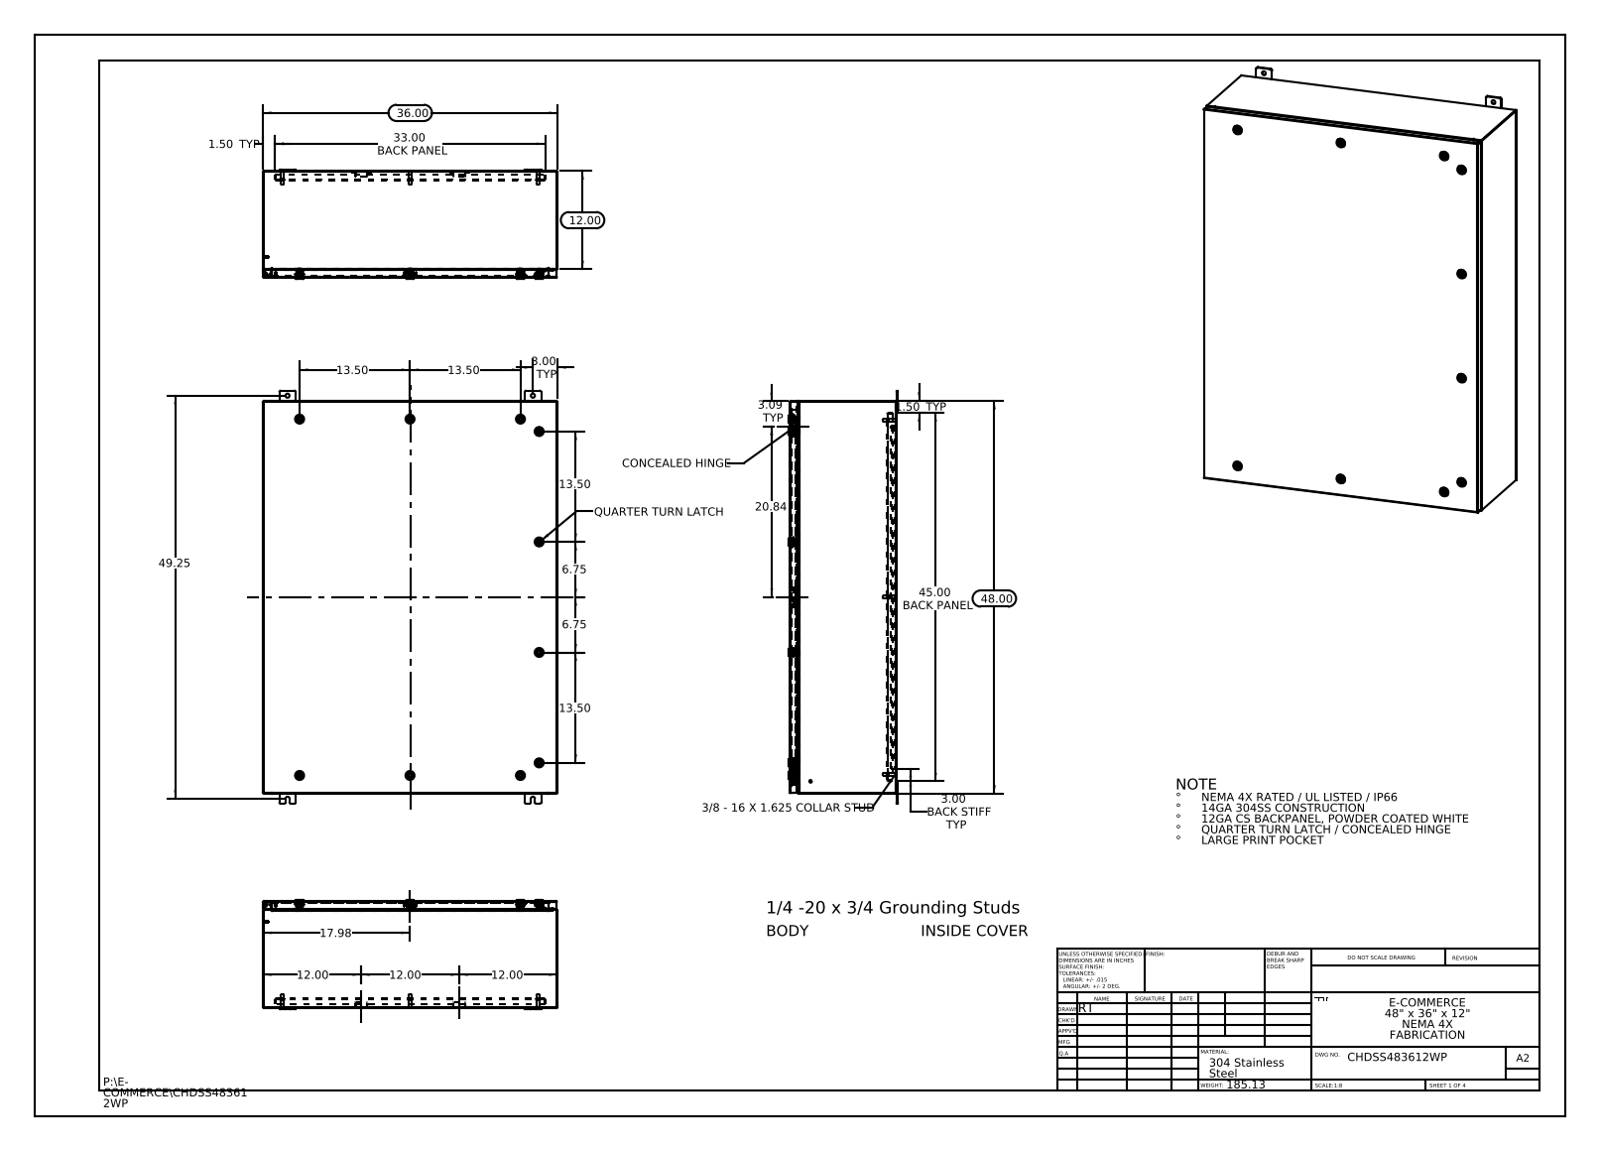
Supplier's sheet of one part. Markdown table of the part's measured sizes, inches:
| quantity | value |
| --- | --- |
| part name | CHDSS483612WP Enclosure Stiffener; Concealed Hinge (Cover Side); CHDSS483612WP Cover; Concealed Hinge enclosure side (+8 more) |
| STEP written by | SolidWorks 2013 (CONFIG_CONTROL_DESIGN) |
| units | inches |
| bodies | 94 solids, 9060 faces (2626 planar, 2826 cylindrical, 3608 other) |
| overall size | 50.5 × 36 × 13.356 |
| volume | 653.3 in³ |
| surface area | 16 243 in² |
| round holes (diameter × count) | 0.5 × 12, 0.197 × 10, 0.394 × 10, 0.4 × 10, 0.63 × 10, 0.787 × 10, 0.136 × 6, 0.25 × 6, 0.211 × 1 |
| round bosses / shafts (diameter × count) | 0.236 × 12, 1.102 × 10, 0.78 × 10, 0.626 × 10, 0.61 × 10, 0.531 × 10, 0.392 × 10, 0.114 × 10 |
| partial cylindrical surfaces (radius × count) | 0.006 × 330, 0.118 × 330, 0.028 × 120, 0.02 × 40, 0.197 × 40, 0.013 × 34, 0.088 × 30, 0.19 × 24 |
| main face-to-face distances | 0.075, 0.074, 12.861, 12.936, 13.01, 12.935, 0.104, 1, 1.075, 11.861 |
| hole center spacings | 13.5, 20, 20.123, 21.625, 27, 38.003, 45.594, 45.986 |
